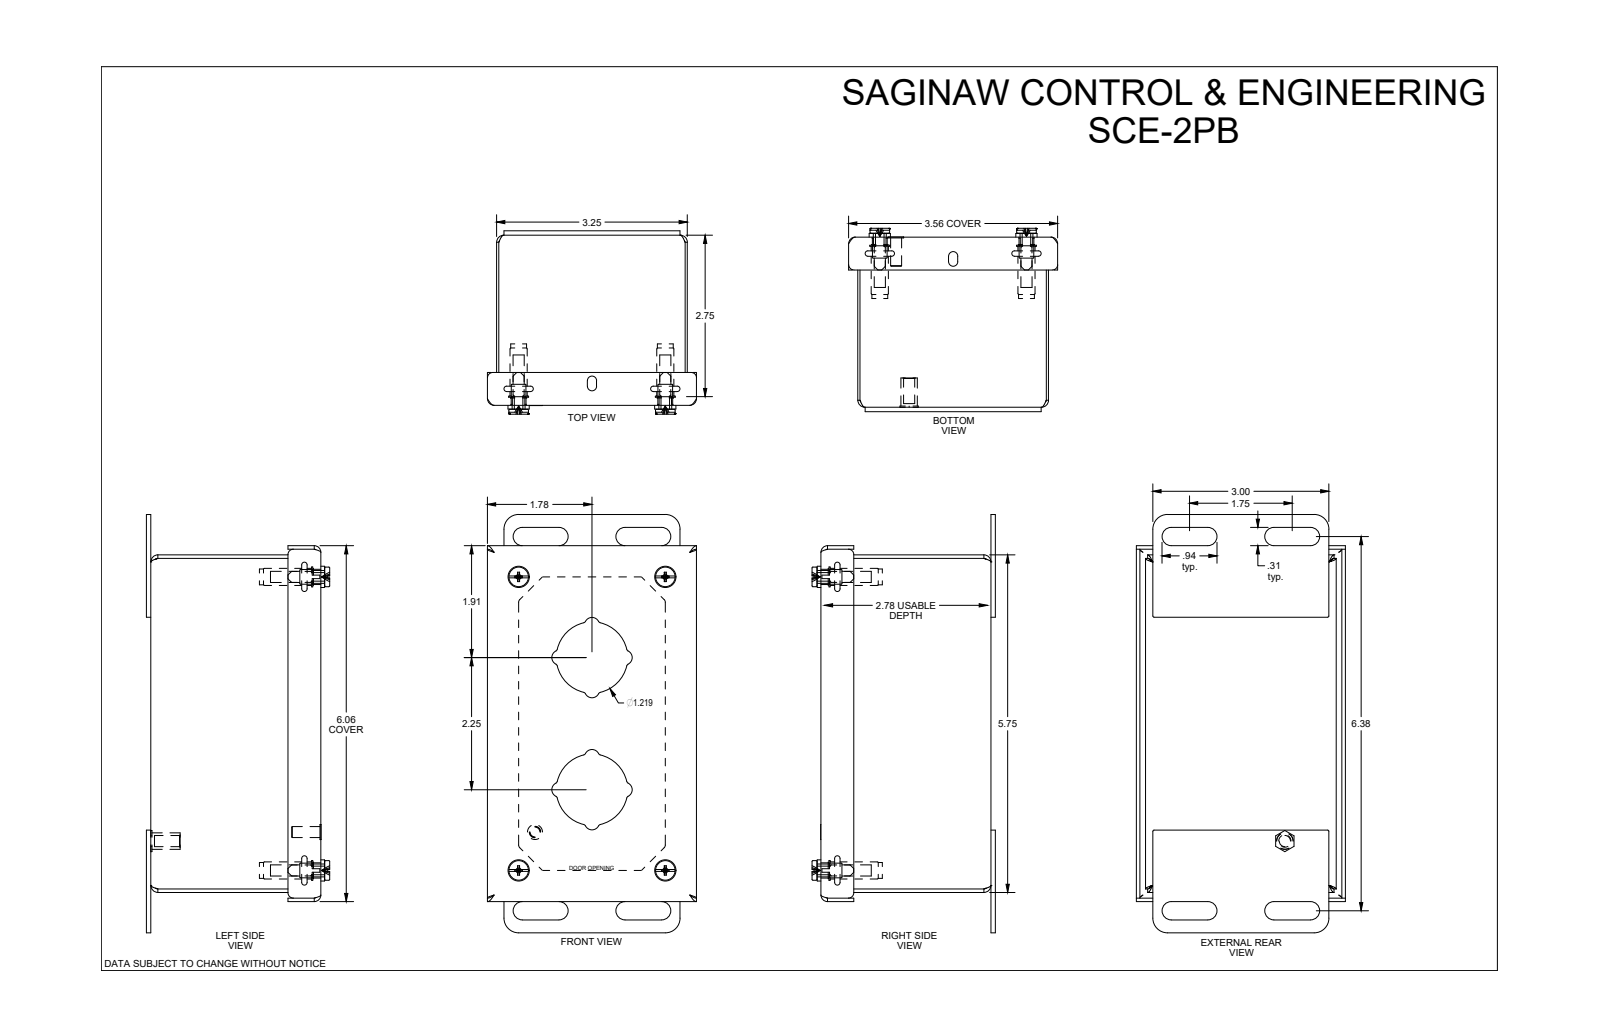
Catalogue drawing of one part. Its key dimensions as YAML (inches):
part_name: "SCE-2PB"
step_written_by: "SolidWorks 2021 (AUTOMOTIVE_DESIGN)"
units: inches
bodies: {solids: 14, faces: 465, planar: 159, cylindrical: 153, other: 153}
overall_size: [7.125, 3.562, 3.124]
volume: 7.112
surface_area: 235.9
round_holes:
  - {diameter: 0.22, count: 4}
  - {diameter: 0.266, count: 4}
  - {diameter: 0.317, count: 4}
round_bosses_or_shafts:
  - {diameter: 0.188, count: 5}
  - {diameter: 0.362, count: 4}
  - {diameter: 0.334, count: 4}
  - {diameter: 0.26, count: 4}
  - {diameter: 0.146, count: 4}
  - {diameter: 0.256, count: 1}
partial_cylinders:
  - {radius: 0.06, count: 20}
  - {radius: 0.04, count: 16}
  - {radius: 0.015, count: 8}
  - {radius: 0.115, count: 8}
  - {radius: 0.125, count: 8}
  - {radius: 0.156, count: 8}
  - {radius: 0.245, count: 8}
  - {radius: 0.02, count: 4}
face_to_face_distances: [0.06, 2.838, 3.19, 2.898, 2.778, 5.69, 0.156, 3.25, 3.13, 3.346]
hole_center_spacings: [2.5, 2.5, 5, 5.59, 5.587, 2.495, 4.996, 4.997]
